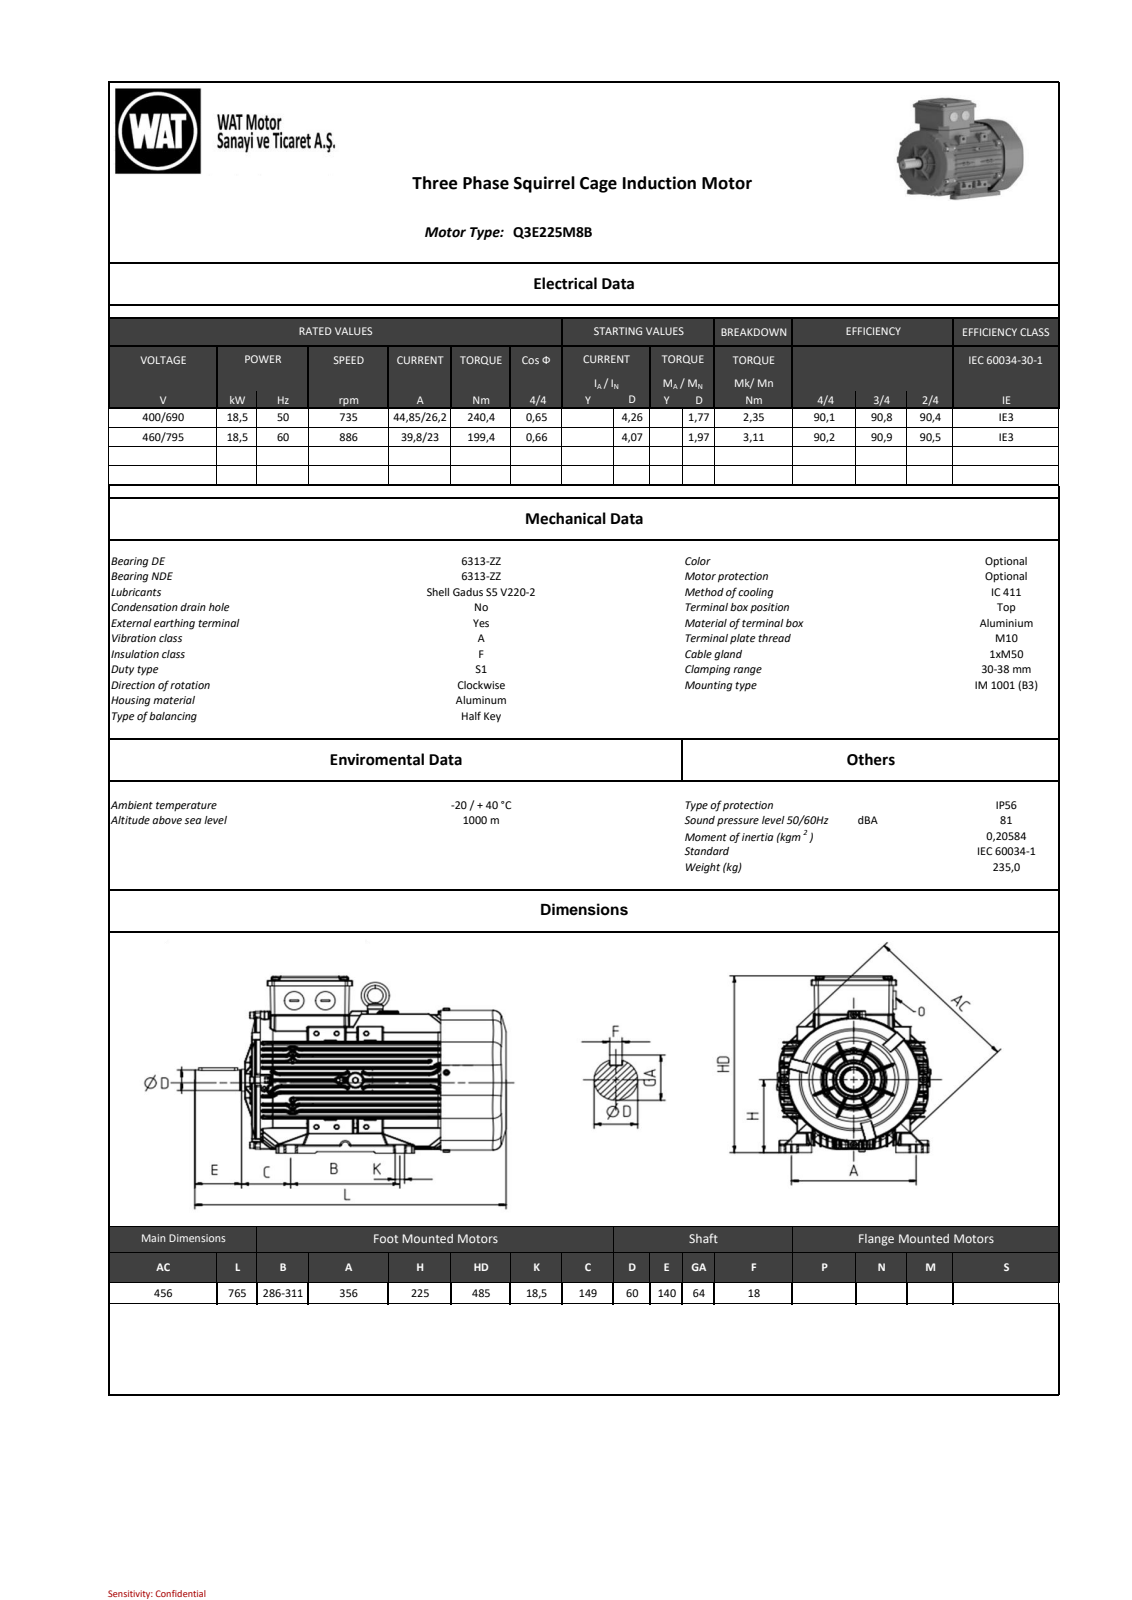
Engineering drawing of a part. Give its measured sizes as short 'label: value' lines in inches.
name: AB_objects
written by: SIEMENS PLM Software NX2206.8101 (AUTOMOTIVE_DESIGN)
unit: in
bodies: 0 solids, 15089 faces (6626 planar, 2843 cylindrical, 5620 other)
size: 30.039 × 19.98 × 17.402
holes: 8× ⌀0.413, 7× ⌀0.197, 6× ⌀0.028, 5× ⌀0.236, 5× ⌀0.295, 4× ⌀0.169, 4× ⌀0.217, 4× ⌀0.256, 4× ⌀0.33, 3× ⌀0.157, 3× ⌀0.406, 2× ⌀1.555
bosses: 6× ⌀0.394, 4× ⌀0.65, 4× ⌀0.63, 3× ⌀0.23, 2× ⌀2.283, 2× ⌀2.169, 2× ⌀2.059, 2× ⌀2.055
rounds: 820× R0.039, 332× R0.008, 217× R0.079, 166× R0.02, 82× R0.118, 81× R0.197, 76× R0.098, 44× R0.984
face distances: 7.473, 0.611, 0.197, 6.655, 0.818, 0.584, 7.267, 0.206, 0.97, 5.915
hole spacings: 0.291, 6.142, 5.761, 2.684, 5.354, 0.505, 3.077, 6.163
